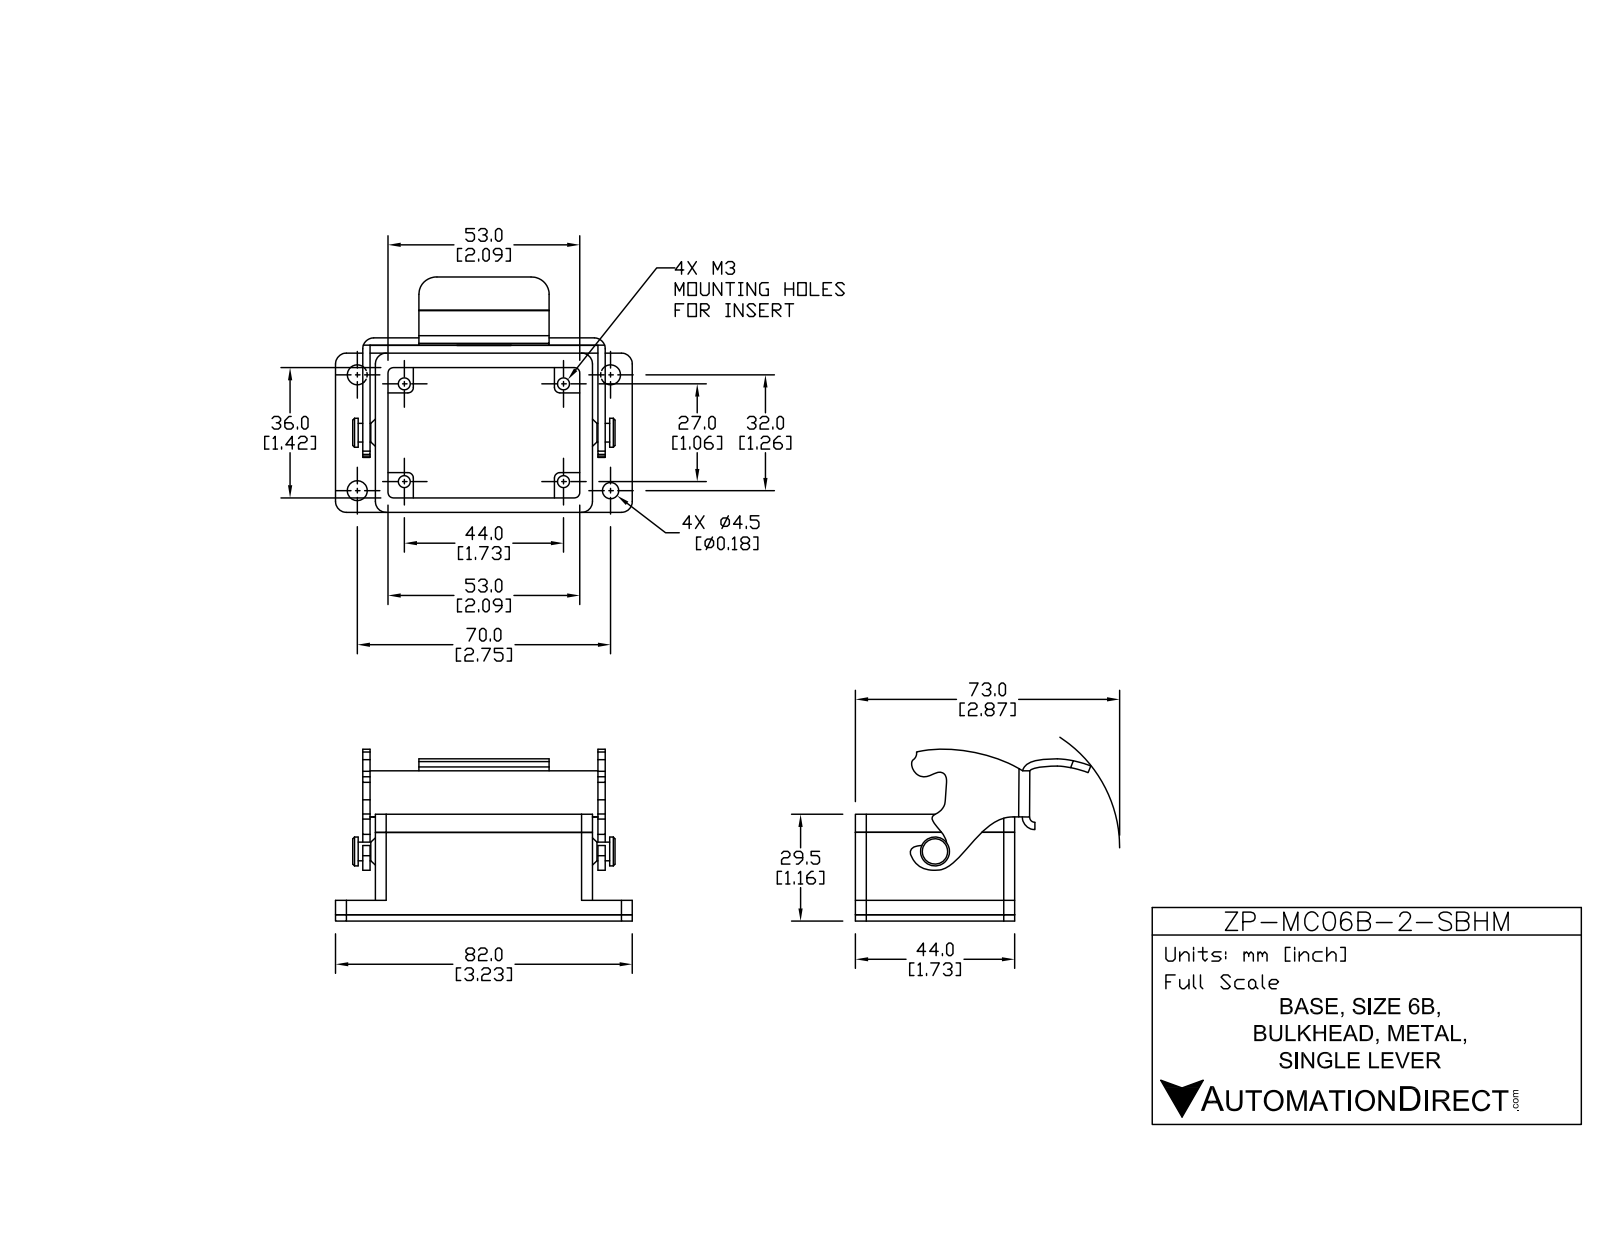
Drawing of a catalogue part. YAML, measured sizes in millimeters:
part_name: "ZP-MC06B-2-SBHM"
step_written_by: "SolidWorks 2011 (AUTOMOTIVE_DESIGN)"
units: millimeters
bodies: {solids: 2, faces: 230, planar: 87, cylindrical: 125, other: 18}
overall_size: [82, 57.88, 55.34]
volume: 31839
surface_area: 25523
round_holes:
  - {diameter: 3.5, count: 4}
  - {diameter: 4.5, count: 4}
round_bosses_or_shafts:
  - {diameter: 8, count: 1}
  - {diameter: 5.17, count: 1}
partial_cylinders:
  - {radius: 3, count: 9}
  - {radius: 0.13, count: 8}
  - {radius: 1.5, count: 8}
  - {radius: 0.5, count: 7}
  - {radius: 1, count: 6}
  - {radius: 1.53, count: 4}
  - {radius: 2.97, count: 4}
  - {radius: 0.59, count: 3}
face_to_face_distances: [4, 40, 1.75, 56.5, 44, 4.75, 3.5, 61.25, 3.97, 1.25]
hole_center_spacings: [13.15, 32.7, 57.04, 64.41, 28, 32, 44, 52.15]
